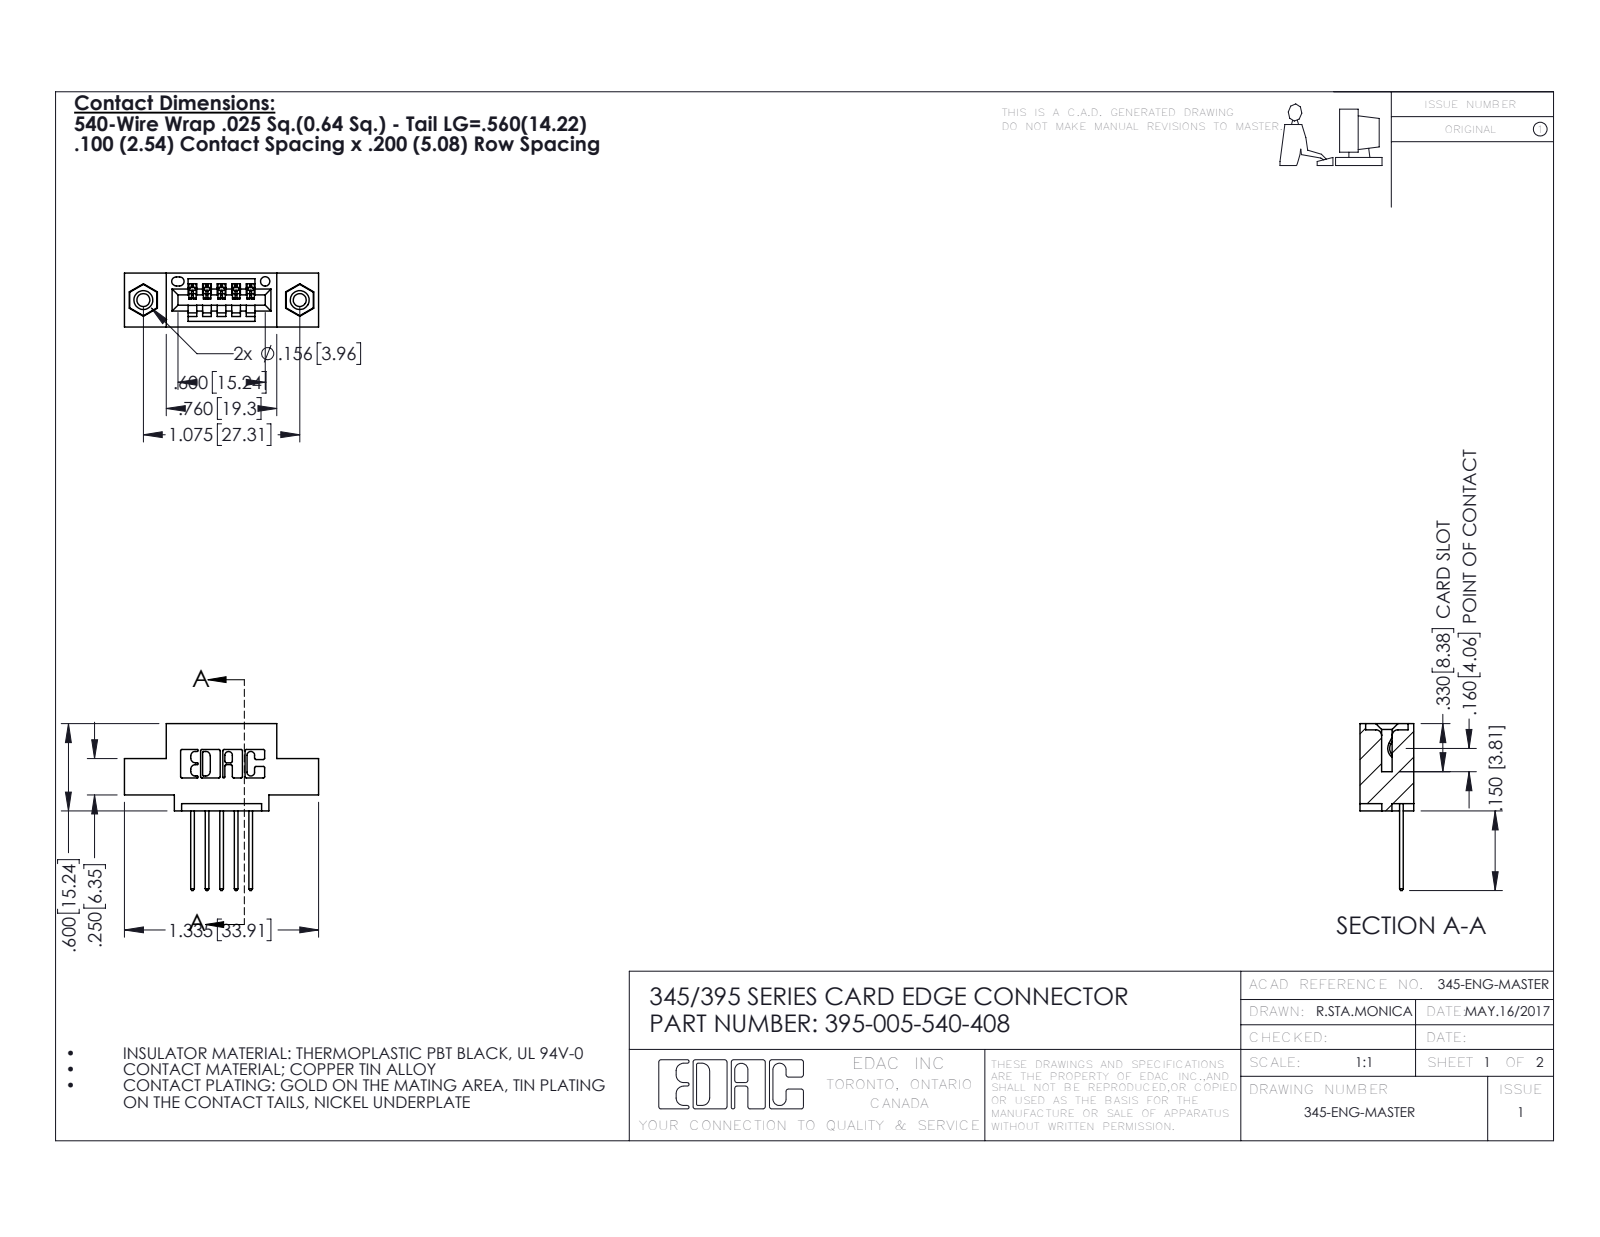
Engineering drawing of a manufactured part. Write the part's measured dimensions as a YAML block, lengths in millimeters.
part_name: "395-005-540-408; 345-250-001_345-250-003-102; 345 Part_0.110 Offset - 0.156 Dia-TI; 345-292-001_345-293-140"
step_written_by: "SolidWorks 2016 (CONFIG_CONTROL_DESIGN)"
units: millimeters
bodies: {solids: 8, faces: 480, planar: 316, cylindrical: 148, other: 16}
overall_size: [33.9, 29.1, 9.4]
volume: 2850
surface_area: 3427
round_holes:
  - {diameter: 2.3, count: 2}
  - {diameter: 3.2, count: 2}
  - {diameter: 4, count: 2}
  - {diameter: 1.6, count: 1}
round_bosses_or_shafts:
  - {diameter: 3.9, count: 2}
partial_cylinders:
  - {radius: 0.3, count: 22}
  - {radius: 0.2, count: 10}
  - {radius: 0.3, count: 10}
  - {radius: 0.2, count: 6}
  - {radius: 0.8, count: 6}
  - {radius: 0.7, count: 3}
  - {radius: 0.8, count: 2}
  - {radius: 1, count: 2}
face_to_face_distances: [5.1, 9.4, 1.8, 7.6, 2.5, 0.6, 2.5, 6.9, 6.4, 1.5]
hole_center_spacings: [6.9, 21.5, 27.3]
